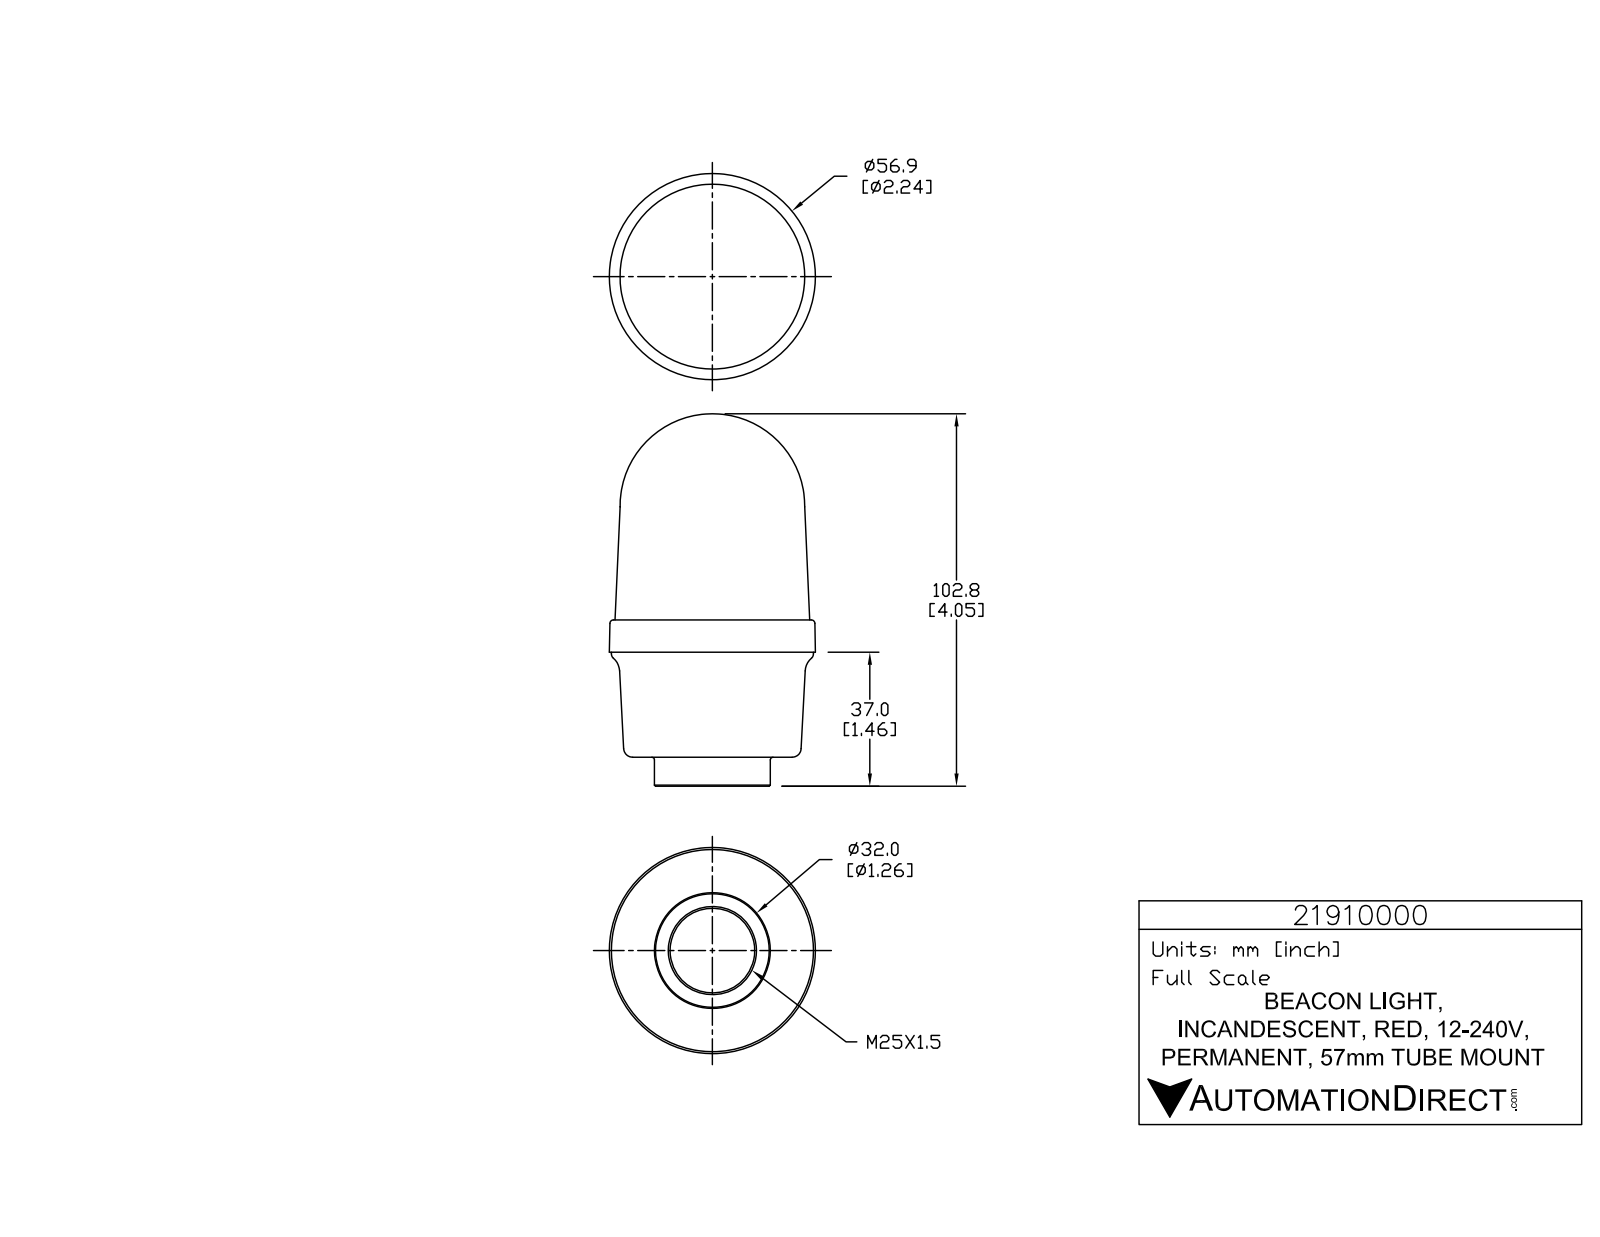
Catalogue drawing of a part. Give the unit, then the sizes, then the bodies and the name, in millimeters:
Units: millimetres
Overall size (bounding box): 102.8 × 56.9 × 56.9
Round holes (diameter × count): ⌀0.99 ×3, ⌀23.38 ×1
Round bosses / shafts (diameter × count): ⌀5.74 ×3, ⌀1.43 ×3, ⌀55.8 ×1, ⌀32 ×1
Partial cylindrical surfaces — rounded edges, fillets, slot ends (radius × count): R0.2 ×6, R0.21 ×6, R0.21 ×6, R3.32 ×6, R0.1 ×3, R0.12 ×3, R0.19 ×3, R0.2 ×3
Main face-to-face distances: 8, 29, 37, 8.9, 37.9, 45.9, 10.61, 19.51, 48.51, 56.51
Volume: 186 111 mm³ · Surface area: 18 965 mm²
Bodies: 1 solid, 764 faces (524 planar, 145 cylindrical, 95 other)
Part name (STEP PRODUCT): 21910000
STEP written by: SolidWorks 2015 (AUTOMOTIVE_DESIGN)
